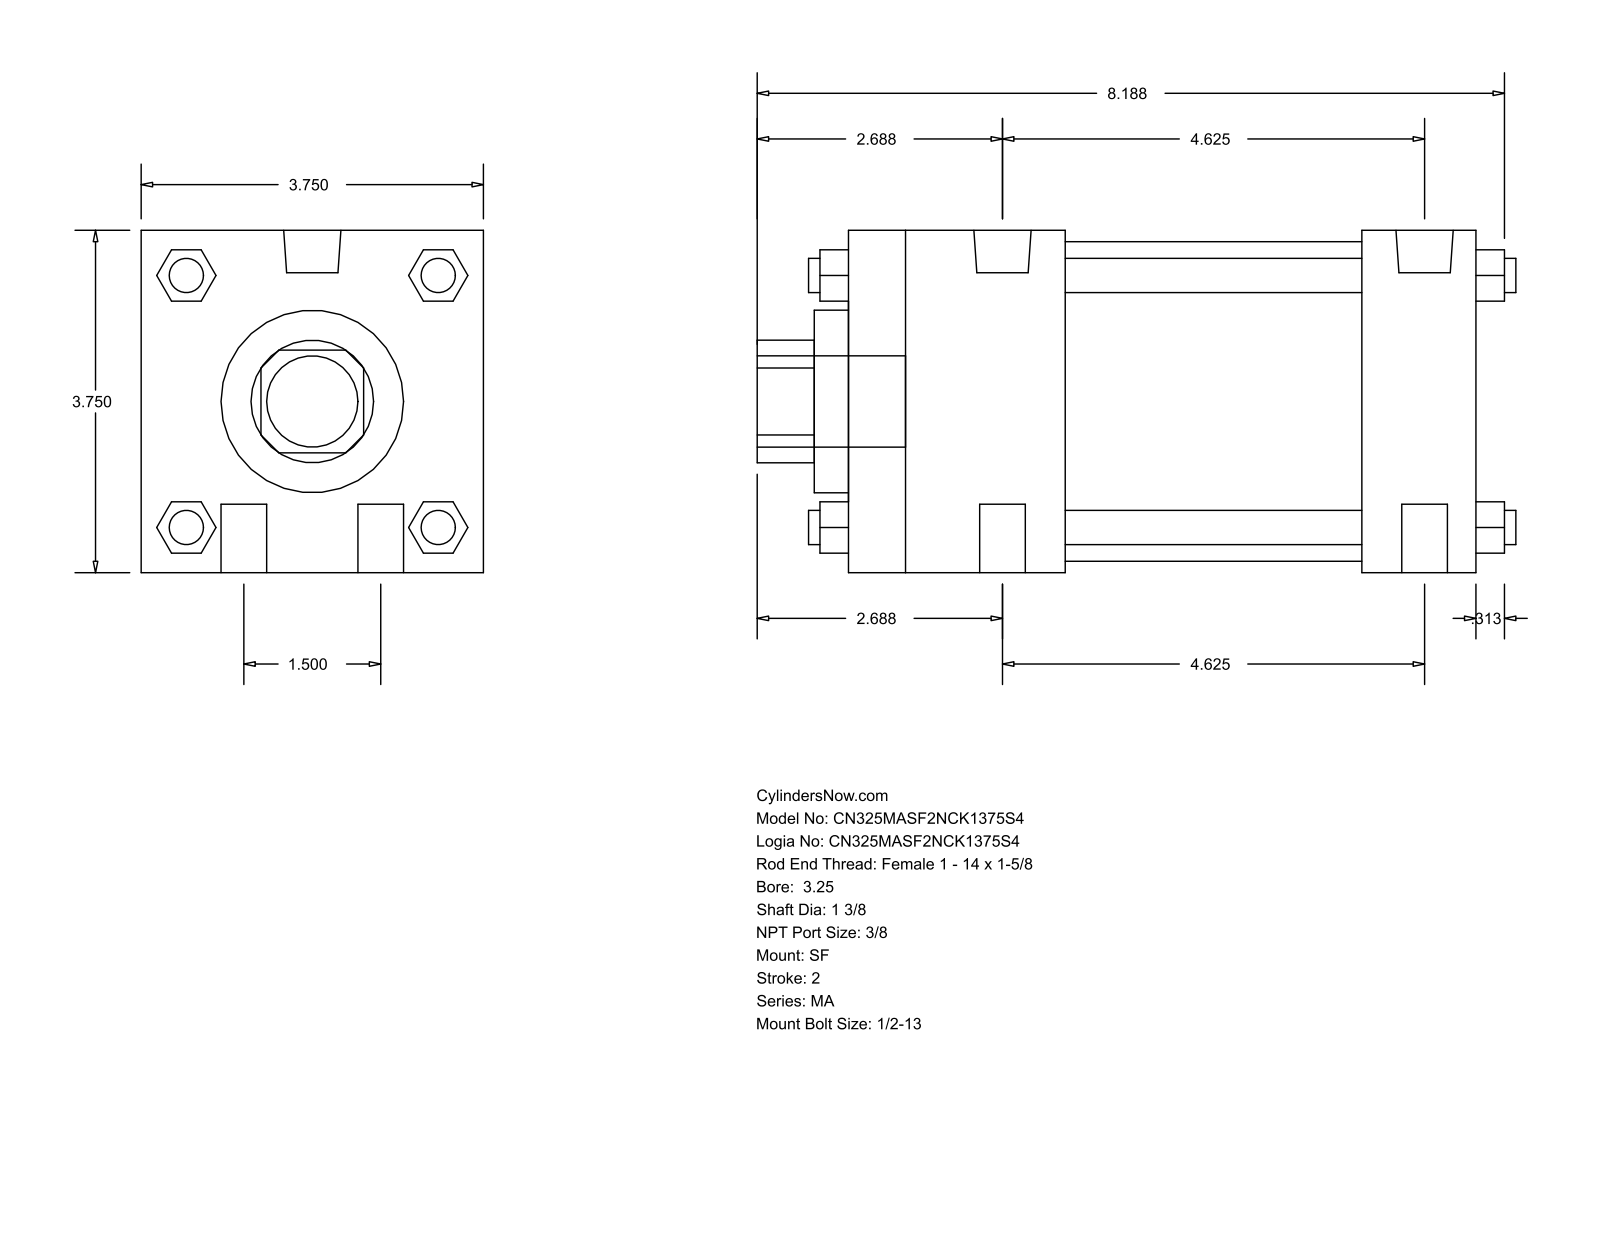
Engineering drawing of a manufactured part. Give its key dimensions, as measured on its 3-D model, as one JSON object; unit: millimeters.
{"part_name": "MA_SF__0325_1.375", "step_written_by": "GSSL Pune (CONFIG_CONTROL_DESIGN)", "units": "millimeters", "bodies": {"solids": 0, "faces": 124, "planar": 94, "cylindrical": 30, "other": 0}, "overall_size": [211.14, 95.25, 95.25], "round_holes": [[34.92, 1], [50.8, 1], [88.9, 1]], "round_bosses_or_shafts": [[12.7, 4], [9.53, 4], [15.93, 2], [11.11, 2], [25.4, 1]], "partial_cylinders_radius": [[17.06, 1]], "face_to_face_distances": [95.24, 174.63, 142.88, 31.75, 60.32, 82.56, 114.31, 9.52, 69.84, 152.4]}
